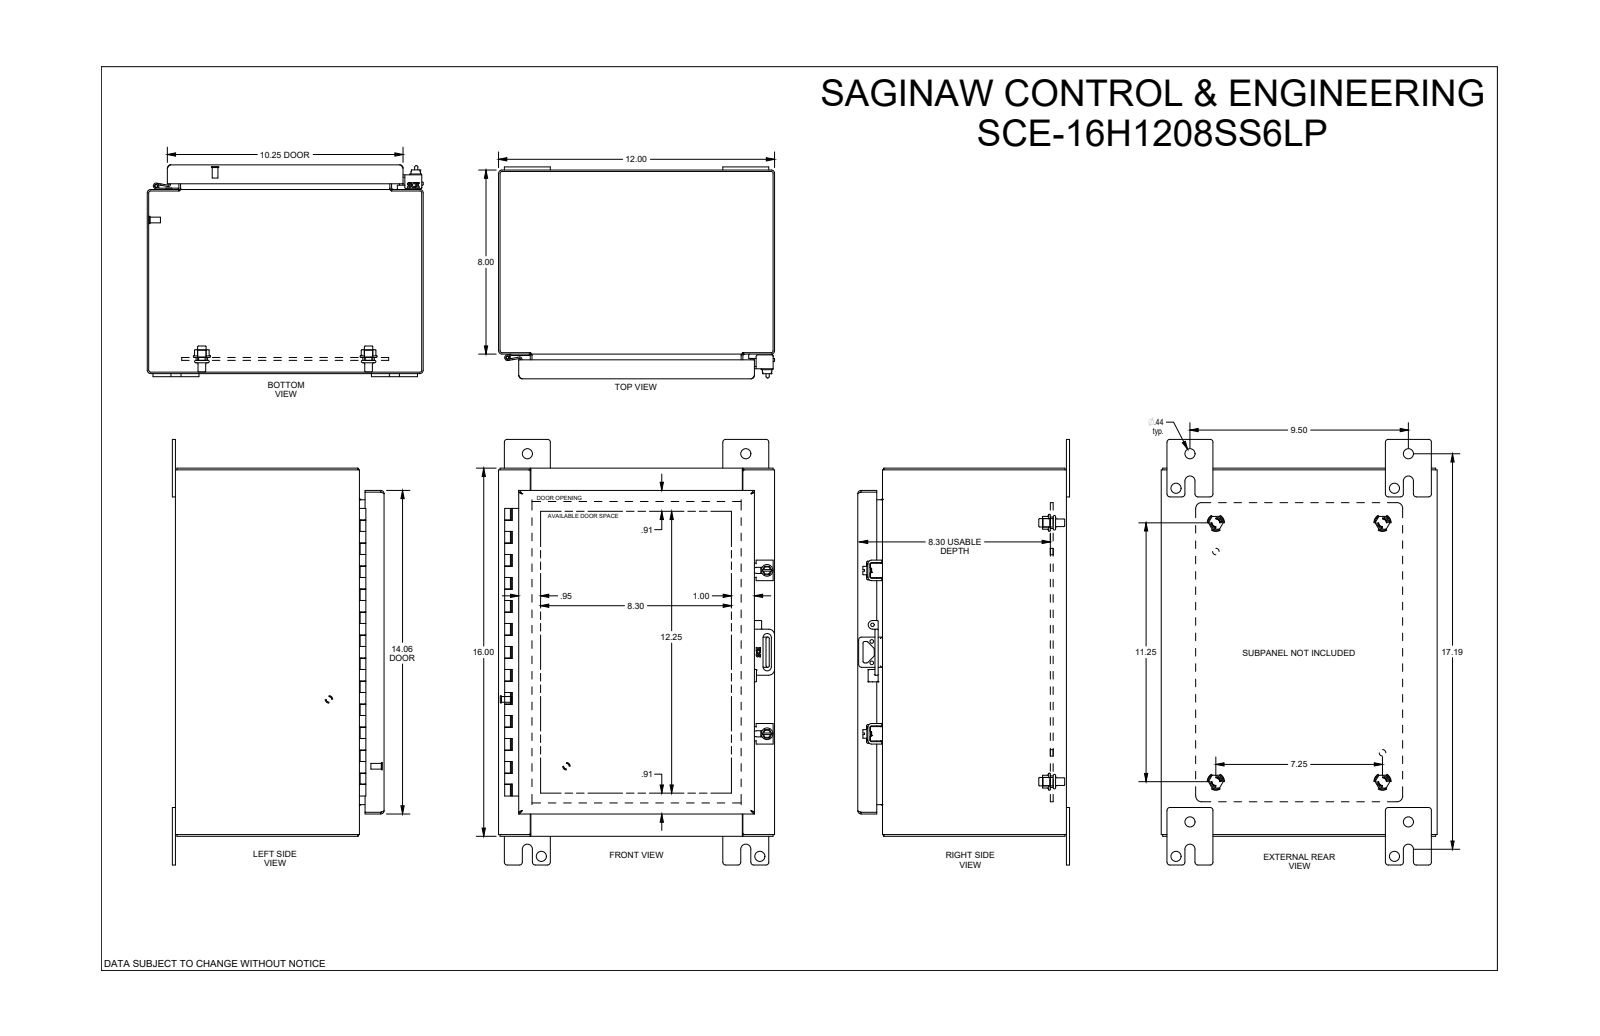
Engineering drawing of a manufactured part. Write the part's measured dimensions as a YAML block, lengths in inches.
part_name: "SCE-16H1208LP"
step_written_by: "SolidWorks 2019 (AUTOMOTIVE_DESIGN)"
units: inches
bodies: {solids: 56, faces: 3444, planar: 1285, cylindrical: 992, other: 1167}
overall_size: [18.5, 12, 9.348]
volume: 96.14
surface_area: 2318
round_holes:
  - {diameter: 0.172, count: 4}
  - {diameter: 0.205, count: 4}
  - {diameter: 0.244, count: 4}
  - {diameter: 0.266, count: 4}
  - {diameter: 0.31, count: 4}
  - {diameter: 0.312, count: 4}
  - {diameter: 0.367, count: 4}
  - {diameter: 0.375, count: 4}
  - {diameter: 0.437, count: 4}
  - {diameter: 0.5, count: 4}
  - {diameter: 0.25, count: 3}
  - {diameter: 0.04, count: 2}
round_bosses_or_shafts:
  - {diameter: 0.17, count: 7}
  - {diameter: 0.25, count: 6}
  - {diameter: 0.248, count: 5}
  - {diameter: 0.59, count: 4}
  - {diameter: 0.376, count: 4}
  - {diameter: 0.366, count: 4}
  - {diameter: 0.332, count: 4}
  - {diameter: 0.24, count: 4}
partial_cylinders:
  - {radius: 0.025, count: 121}
  - {radius: 0.01, count: 116}
  - {radius: 0.015, count: 56}
  - {radius: 0.063, count: 33}
  - {radius: 0.03, count: 32}
  - {radius: 0.06, count: 30}
  - {radius: 0.062, count: 30}
  - {radius: 0.185, count: 21}
face_to_face_distances: [0.075, 11.925, 0.075, 15.925, 0.06, 9.013, 9.073, 8.998, 8.938, 12]
hole_center_spacings: [9.5, 0.02, 0.493, 0.985, 1.976, 8.531, 12.924, 15.359]
